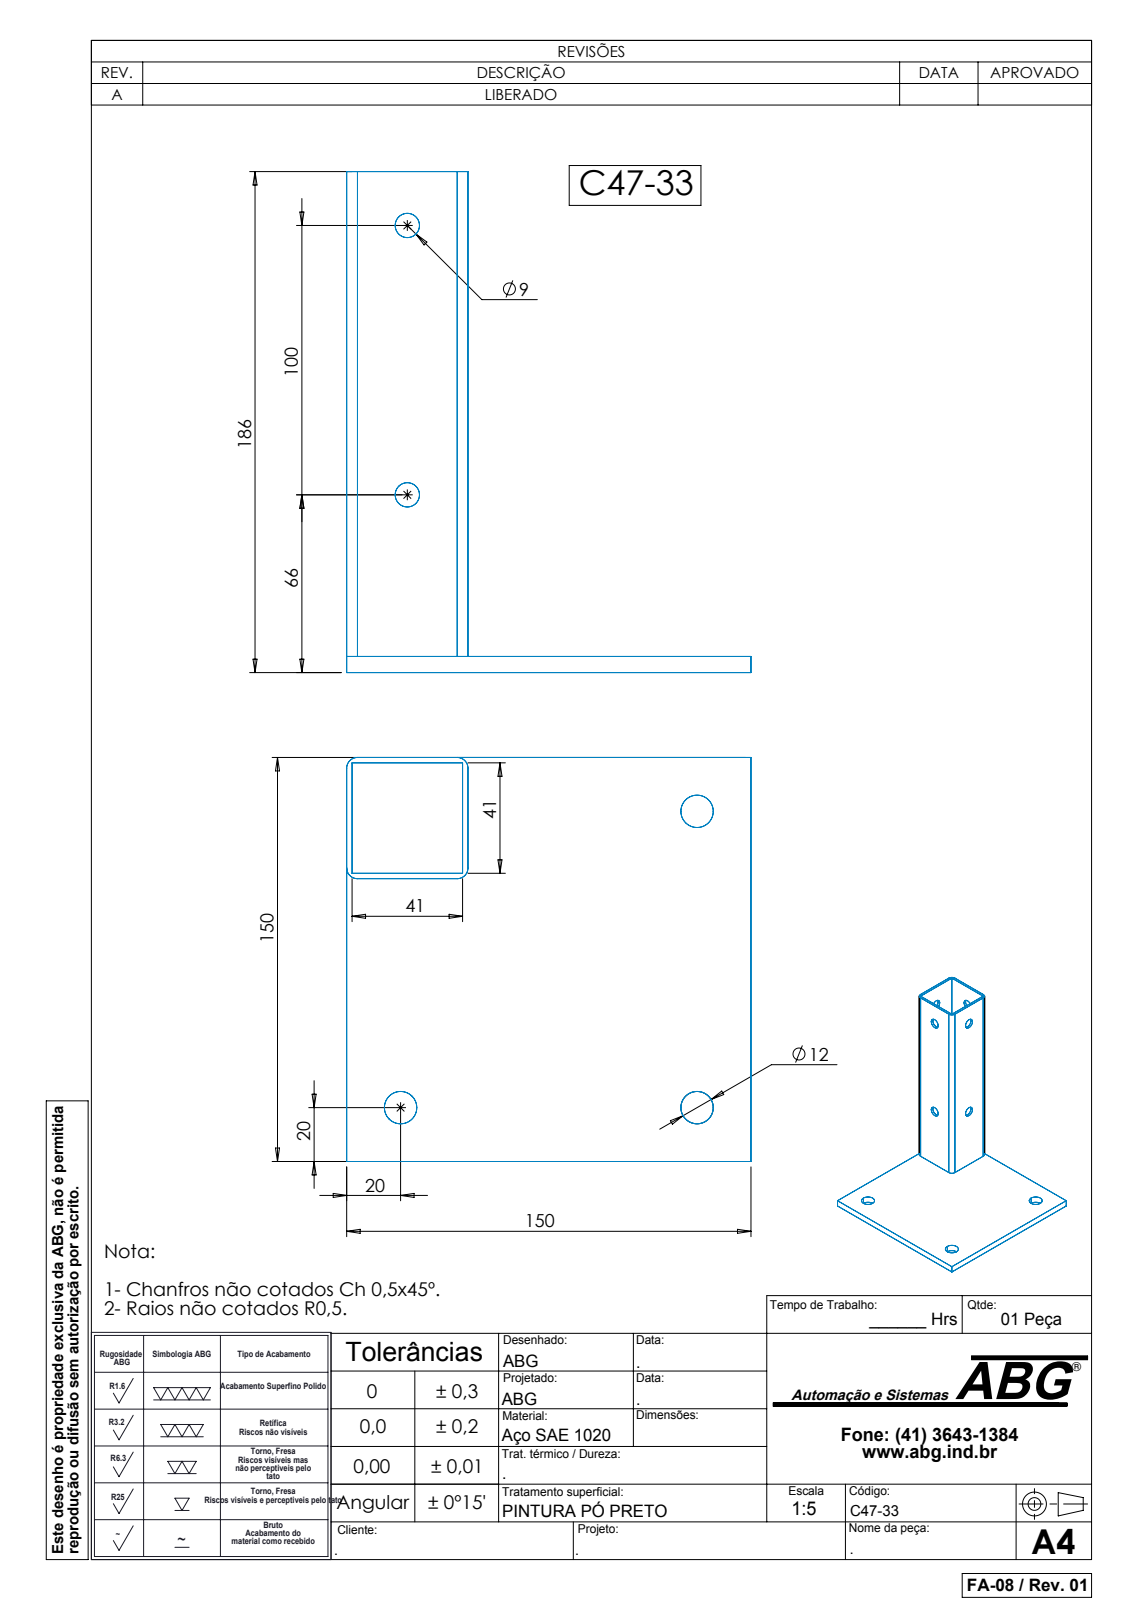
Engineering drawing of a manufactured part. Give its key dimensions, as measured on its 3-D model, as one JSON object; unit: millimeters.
{"part_name": "C47-33", "step_written_by": "SolidWorks 2007 (CONFIG_CONTROL_DESIGN)", "units": "millimeters", "bodies": {"solids": 1, "faces": 40, "planar": 14, "cylindrical": 26, "other": 0}, "overall_size": [186, 150, 150], "volume_mm3": 191374, "surface_area_mm2": 108701, "round_holes": [[9, 4], [12, 3]], "partial_cylinders_radius": [[4, 4]], "face_to_face_distances": [43, 2, 6, 41, 45, 105, 107, 148, 150, 186], "hole_center_spacings": [100, 110, 155.56]}
